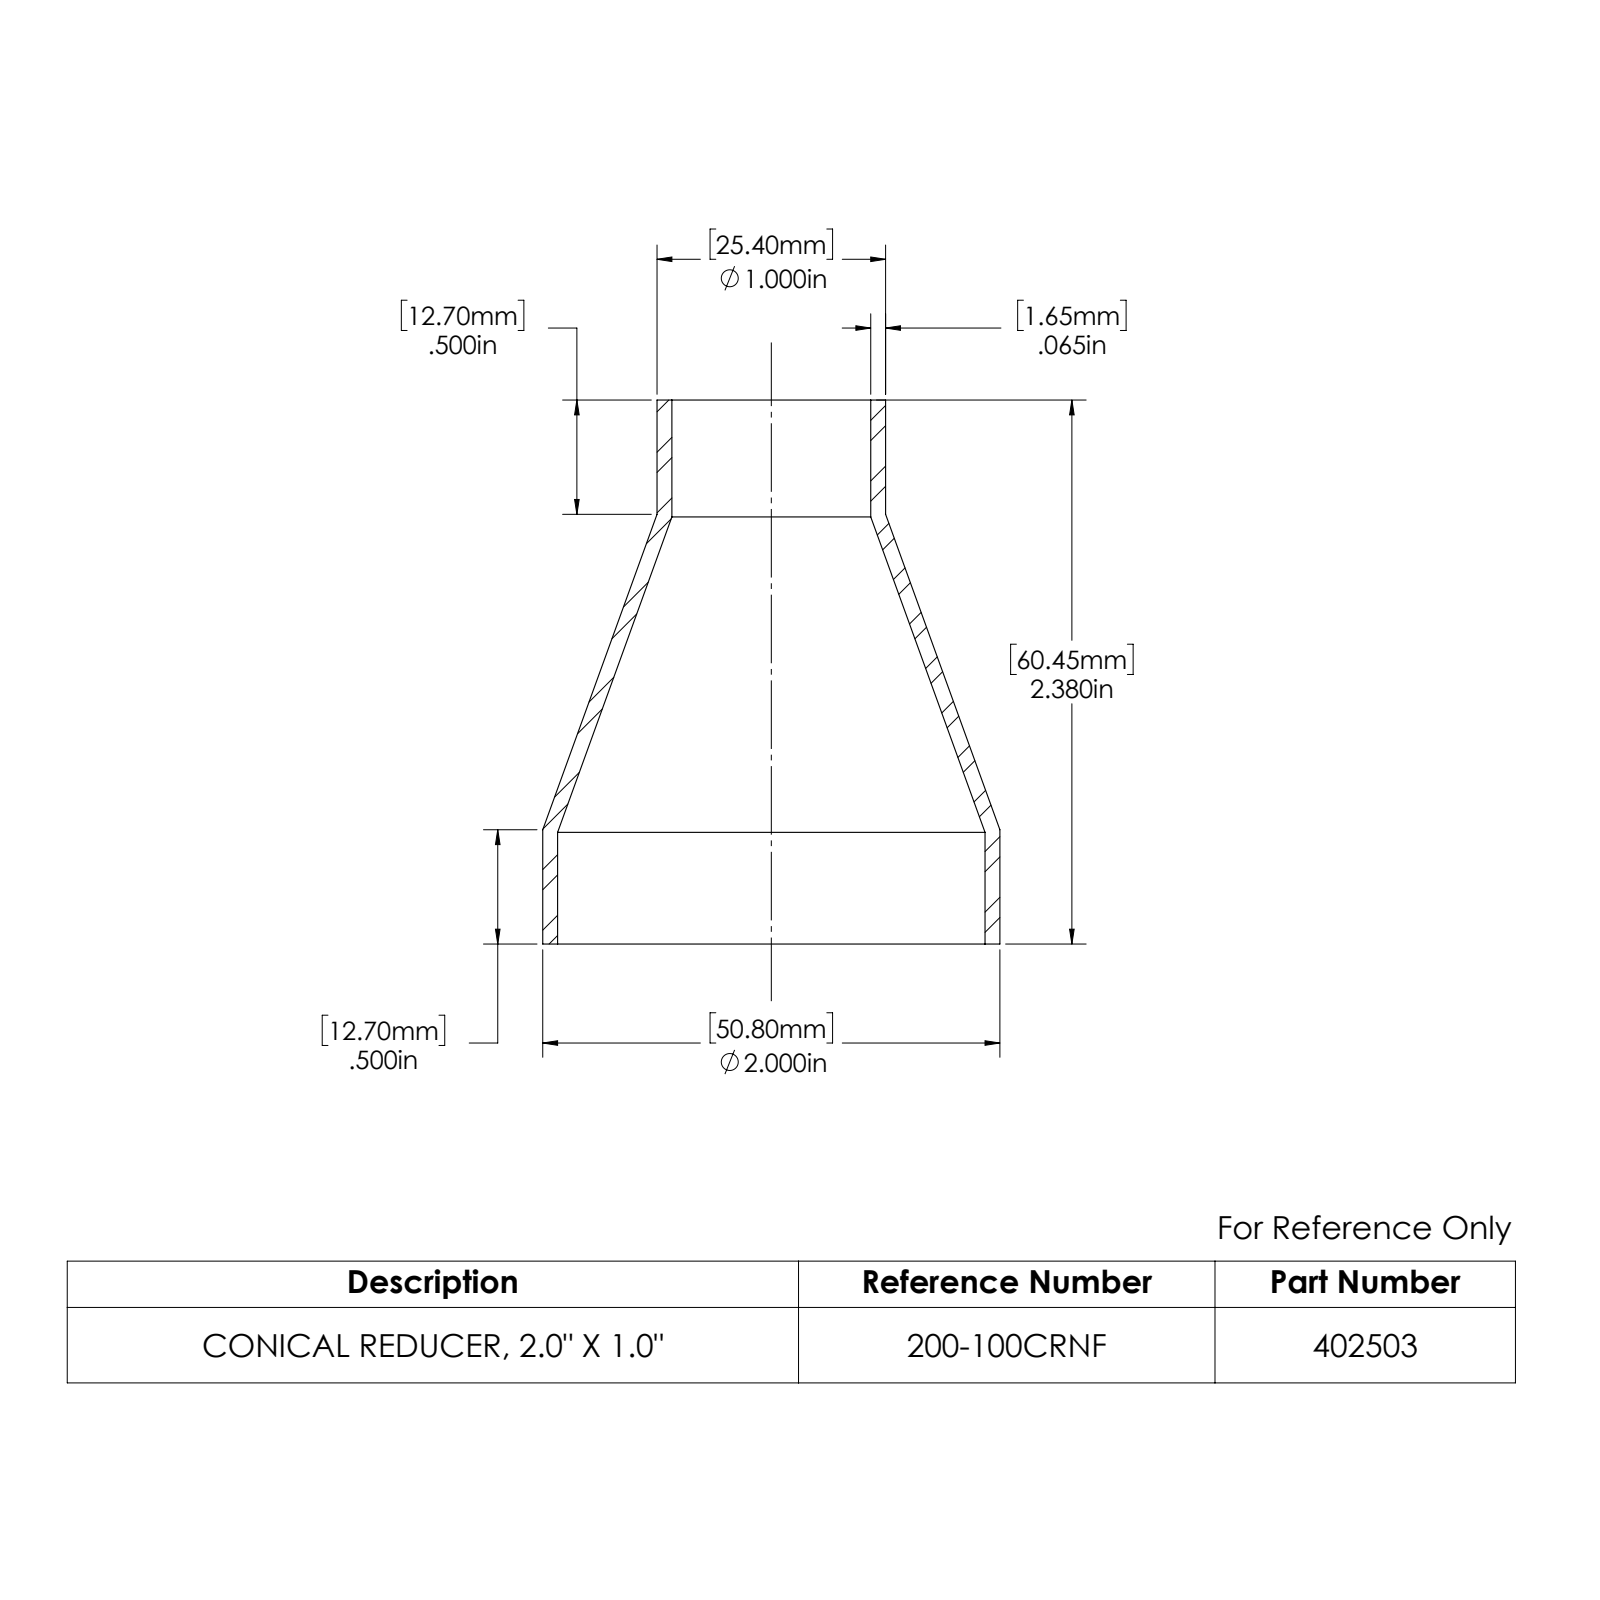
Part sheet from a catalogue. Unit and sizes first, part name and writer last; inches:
Units: inches
Overall size (bounding box): 2.38 × 2 × 2
Round holes (diameter × count): ⌀0.87 ×1, ⌀1.87 ×1
Round bosses / shafts (diameter × count): ⌀2 ×1, ⌀1 ×1
Main face-to-face distances: 2.38
Volume: 0.722 in³ · Surface area: 22.8 in²
Bodies: 1 solid, 14 faces (2 planar, 8 cylindrical, 4 other)
Part name (STEP PRODUCT): 402503
STEP written by: SolidWorks 2022 (AUTOMOTIVE_DESIGN)
